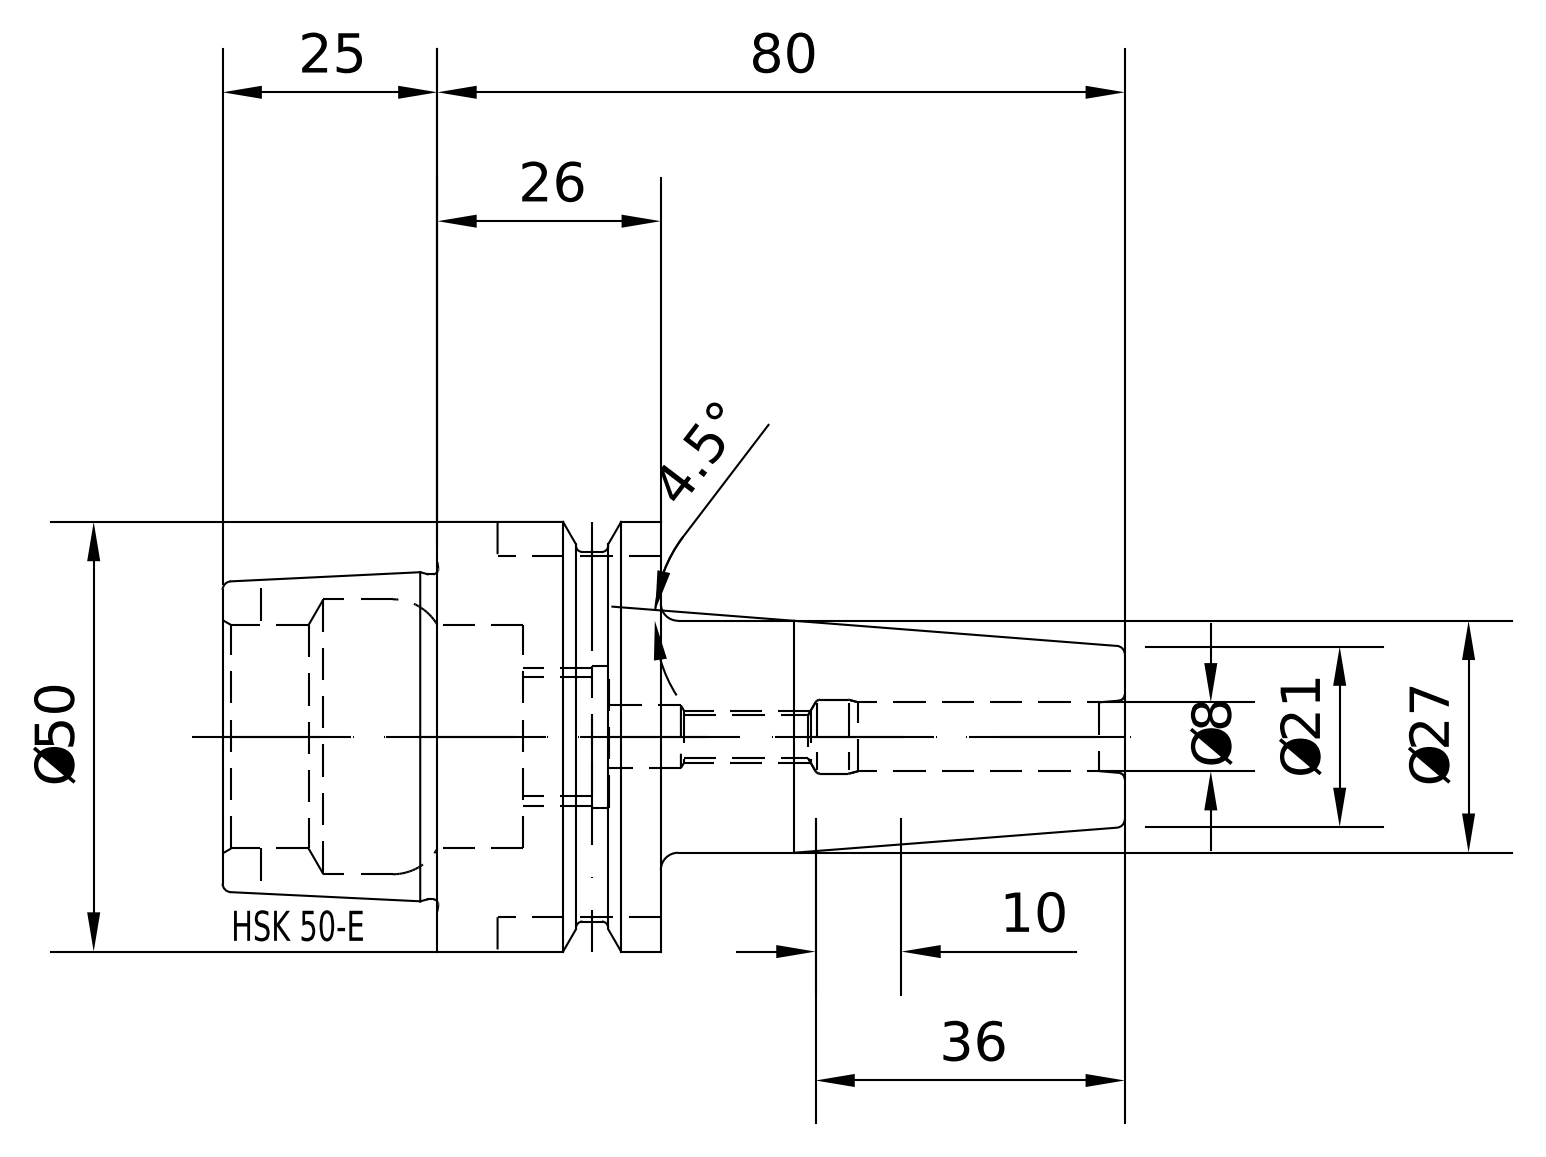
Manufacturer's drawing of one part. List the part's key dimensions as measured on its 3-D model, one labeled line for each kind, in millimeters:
Part name (STEP PRODUCT): E50-140-08
STEP written by: PRO/ENGINEER BY PARAMETRIC TECHNOLOGY CORPORATION, 2010430 (CONFIG_CONTROL_DESIGN)
Units: millimetres
Bodies: 1 solid, 79 faces (9 planar, 24 cylindrical, 46 other)
Overall size (bounding box): 104.9 × 50 × 50
Volume: 76 314 mm³ · Surface area: 19 900 mm²
Round holes (diameter × count): ⌀8 ×1, ⌀14 ×1, ⌀16.32 ×1, ⌀16.5 ×1, ⌀26.04 ×1, ⌀32.08 ×1
Round bosses / shafts (diameter × count): ⌀50 ×1, ⌀42.95 ×1, ⌀37.91 ×1, ⌀27 ×1
Main face-to-face distances: 25.95, 24.9, 50.85, 104.9, 80, 54.05, 34.85, 9.95, 16, 70.05
